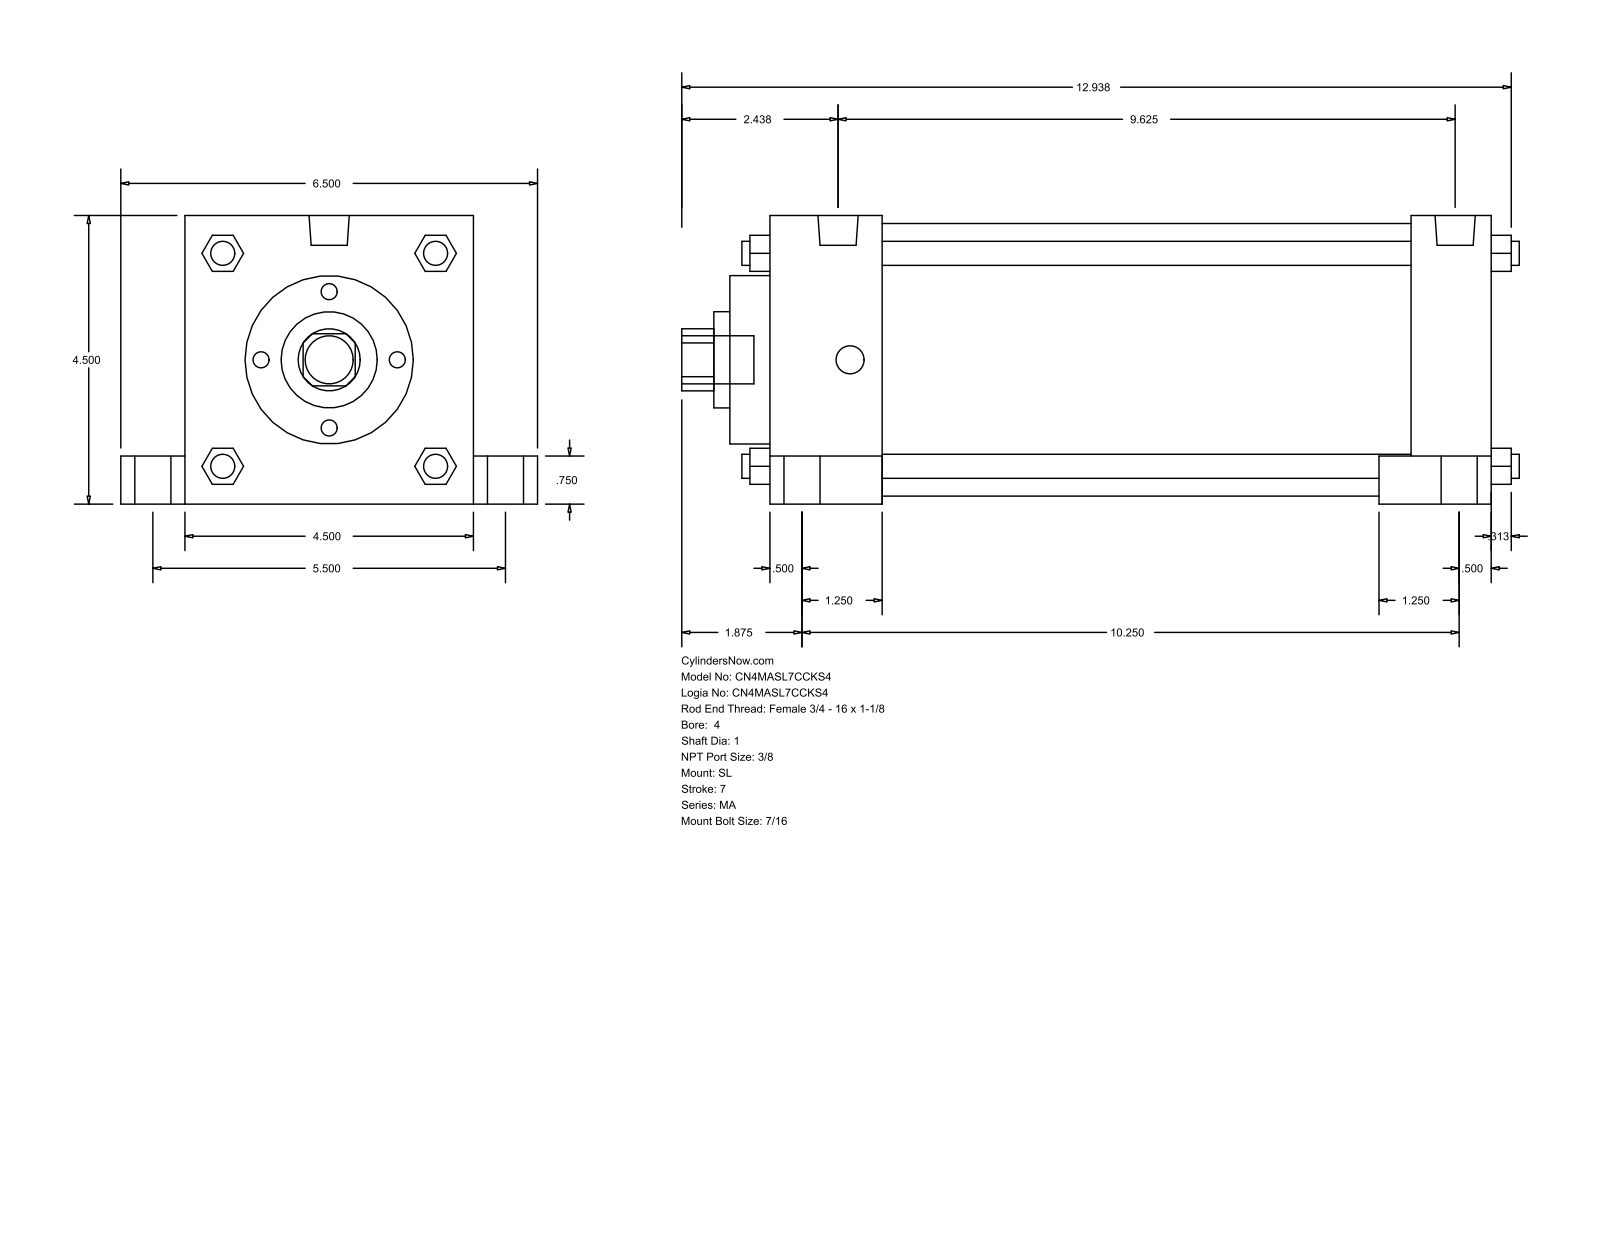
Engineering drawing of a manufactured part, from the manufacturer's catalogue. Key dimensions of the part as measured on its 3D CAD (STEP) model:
Part name (STEP PRODUCT): MA_SL__0400_1
STEP written by: GSSL Pune (CONFIG_CONTROL_DESIGN)
Units: millimetres
Bodies: 0 solids, 150 faces (113 planar, 37 cylindrical, 0 other)
Overall size (bounding box): 331.79 × 165.1 × 114.3
Round holes (diameter × count): ⌀25.4 ×1, ⌀38.1 ×1, ⌀66.67 ×1, ⌀107.95 ×1
Round bosses / shafts (diameter × count): ⌀20.64 ×4, ⌀14.29 ×4, ⌀11.11 ×4, ⌀9.53 ×4, ⌀15.93 ×2, ⌀19.05 ×1
Partial cylindrical surfaces — rounded edges, fillets, slot ends (radius × count): R12.29 ×1
Main face-to-face distances: 114.3, 285.76, 209.55, 44.46, 241.3, 254.01, 31.75, 25.4, 139.7, 19.05
